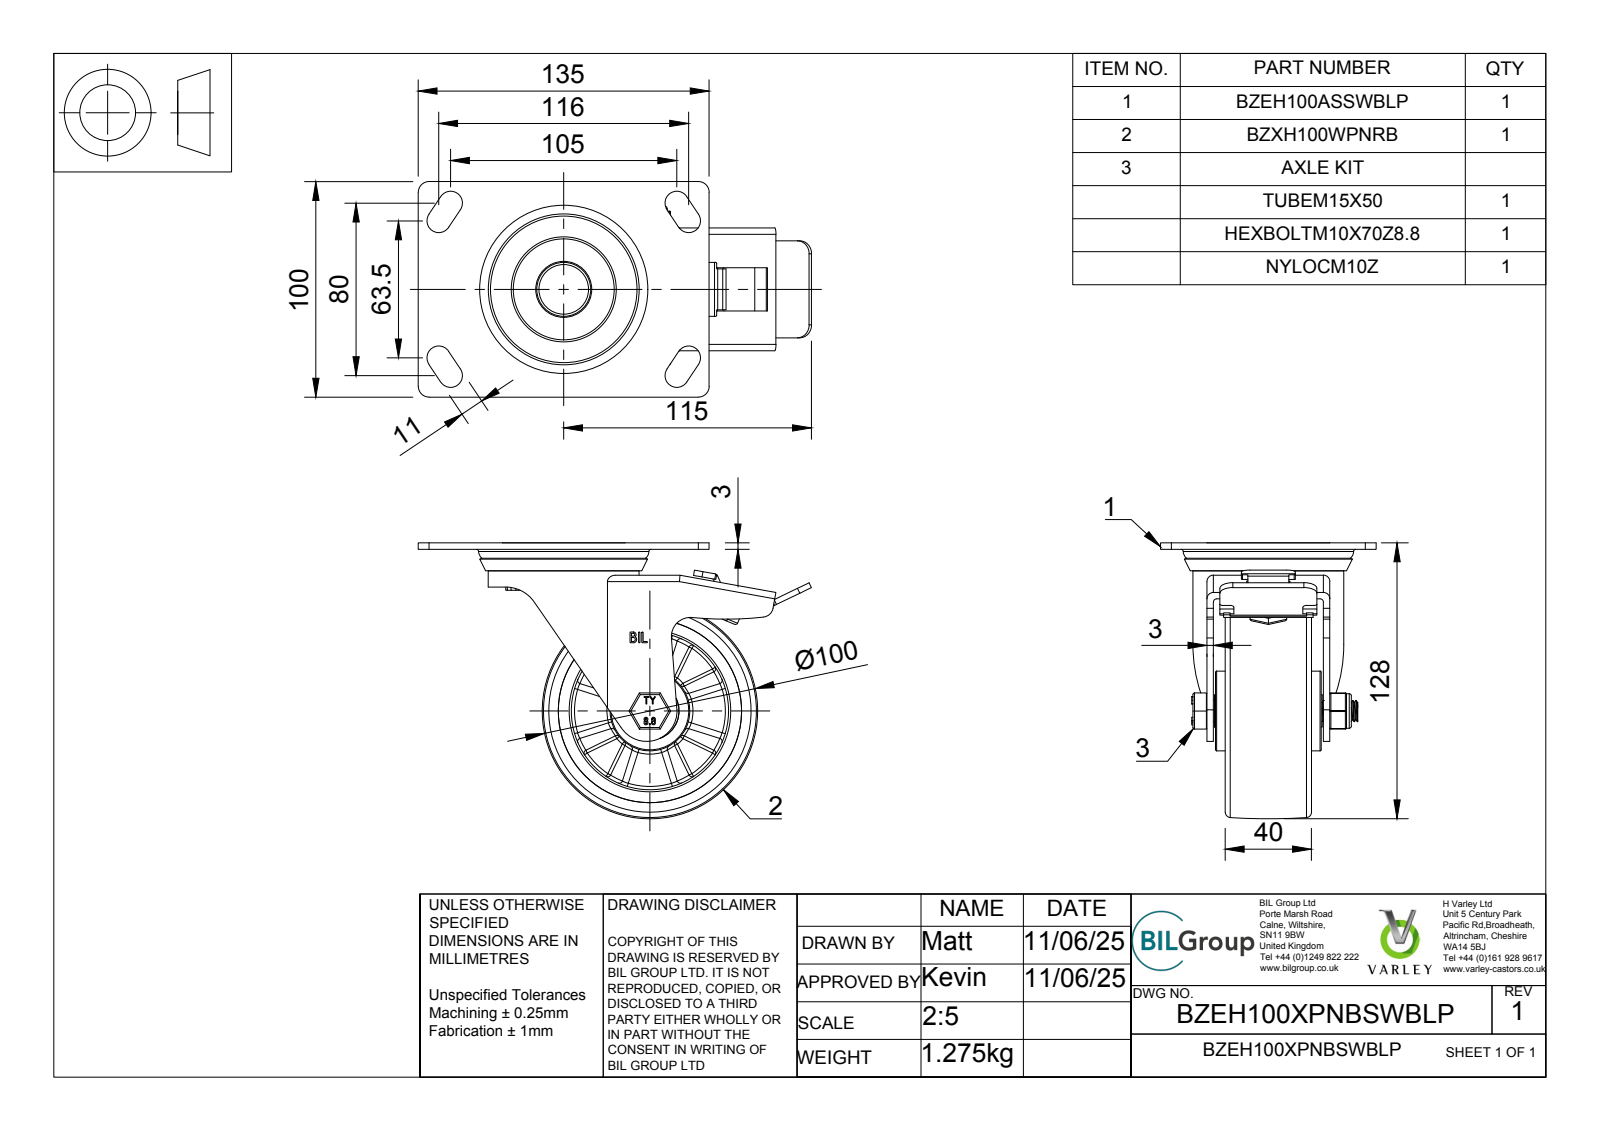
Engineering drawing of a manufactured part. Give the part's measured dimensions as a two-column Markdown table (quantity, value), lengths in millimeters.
| quantity | value |
| --- | --- |
| part name | BZEH100XPNBSWBLP v3; BZEH100ASSWBLP v1; ZINC PLATED, PRESSED STEEL TOP PLATE; ZINC PLATED, PRESSED STEEL TOP PLATE Geometry (+7 more) |
| STEP written by | Autodesk Translation Framework v14.10.0.0 (AUTOMOTIVE_DESIGN) |
| units | millimeters |
| bodies | 42 solids, 882 faces (394 planar, 182 cylindrical, 306 other) |
| overall size | 182.5 × 128 × 100 |
| volume | 347 600 mm³ |
| surface area | 173 429 mm² |
| round holes (diameter × count) | 8 × 1, 10 × 1, 10.2 × 1, 10.5 × 1, 12 × 1, 15 × 1, 15.5 × 1, 26 × 1, 27 × 1, 30 × 1, 64 × 1, 73 × 1 |
| round bosses / shafts (diameter × count) | 4 × 8, 70 × 1, 54 × 1, 37 × 1, 26.9 × 1, 25 × 1, 22.5 × 1, 21 × 1 |
| partial cylindrical surfaces (radius × count) | 0.5 × 20, 1 × 8, 5.5 × 8, 0.75 × 6, 1.5 × 6, 5 × 5, 3 × 4, 2 × 3 |
| main face-to-face distances | 3, 5, 1, 10, 2, 4, 5.5, 7, 54, 8.5 |
